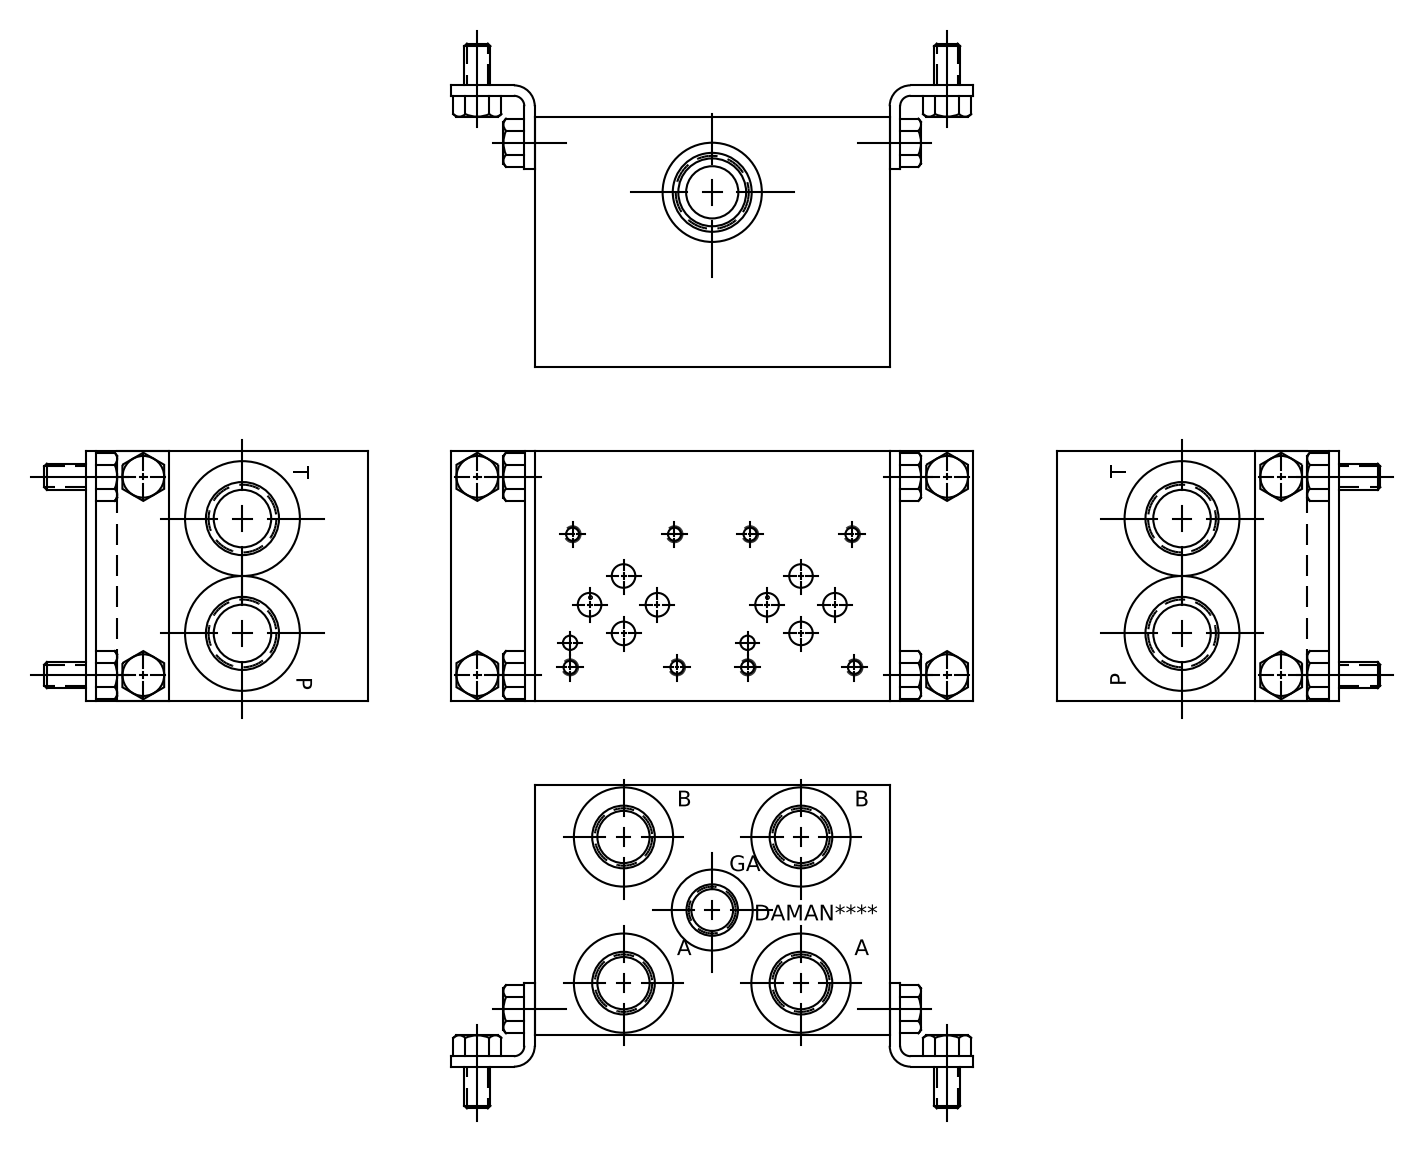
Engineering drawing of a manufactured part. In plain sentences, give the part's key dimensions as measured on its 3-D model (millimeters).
The part is named "Part_AD03P022S_C_3D". Its 3-D file was written by "Autodesk Inventor 2020 (AUTOMOTIVE_DESIGN)". It is 1 solid with 690 faces: 363 planar, 85 cylindrical and 242 other. Overall it measures 107.95 by 76.2 by 76.2 millimeters. Its volume is 534 963 cubic millimeters and its surface area 64 648 square millimeters. Round holes: 8 of diameter 3.78, 8 of diameter 4.83, 6 of diameter 7.14, 4 of diameter 15.88, 4 of diameter 17.5, 4 of diameter 19.05, 4 of diameter 19.25, 4 of diameter 30.63, 3 of diameter 22.23, 2 of diameter 3.96, 2 of diameter 6.35, 2 of diameter 6.53. The main face-to-face distances are 76.2, 107.95, 0.79, 75.41, 107.16, 106.37, 3.17, 73.03, 72.24, 17.45. The hole center spacings are 53.97, 19.95, 22.05, 33.55, 40.49, 51.45, 53.98, 7.49.
